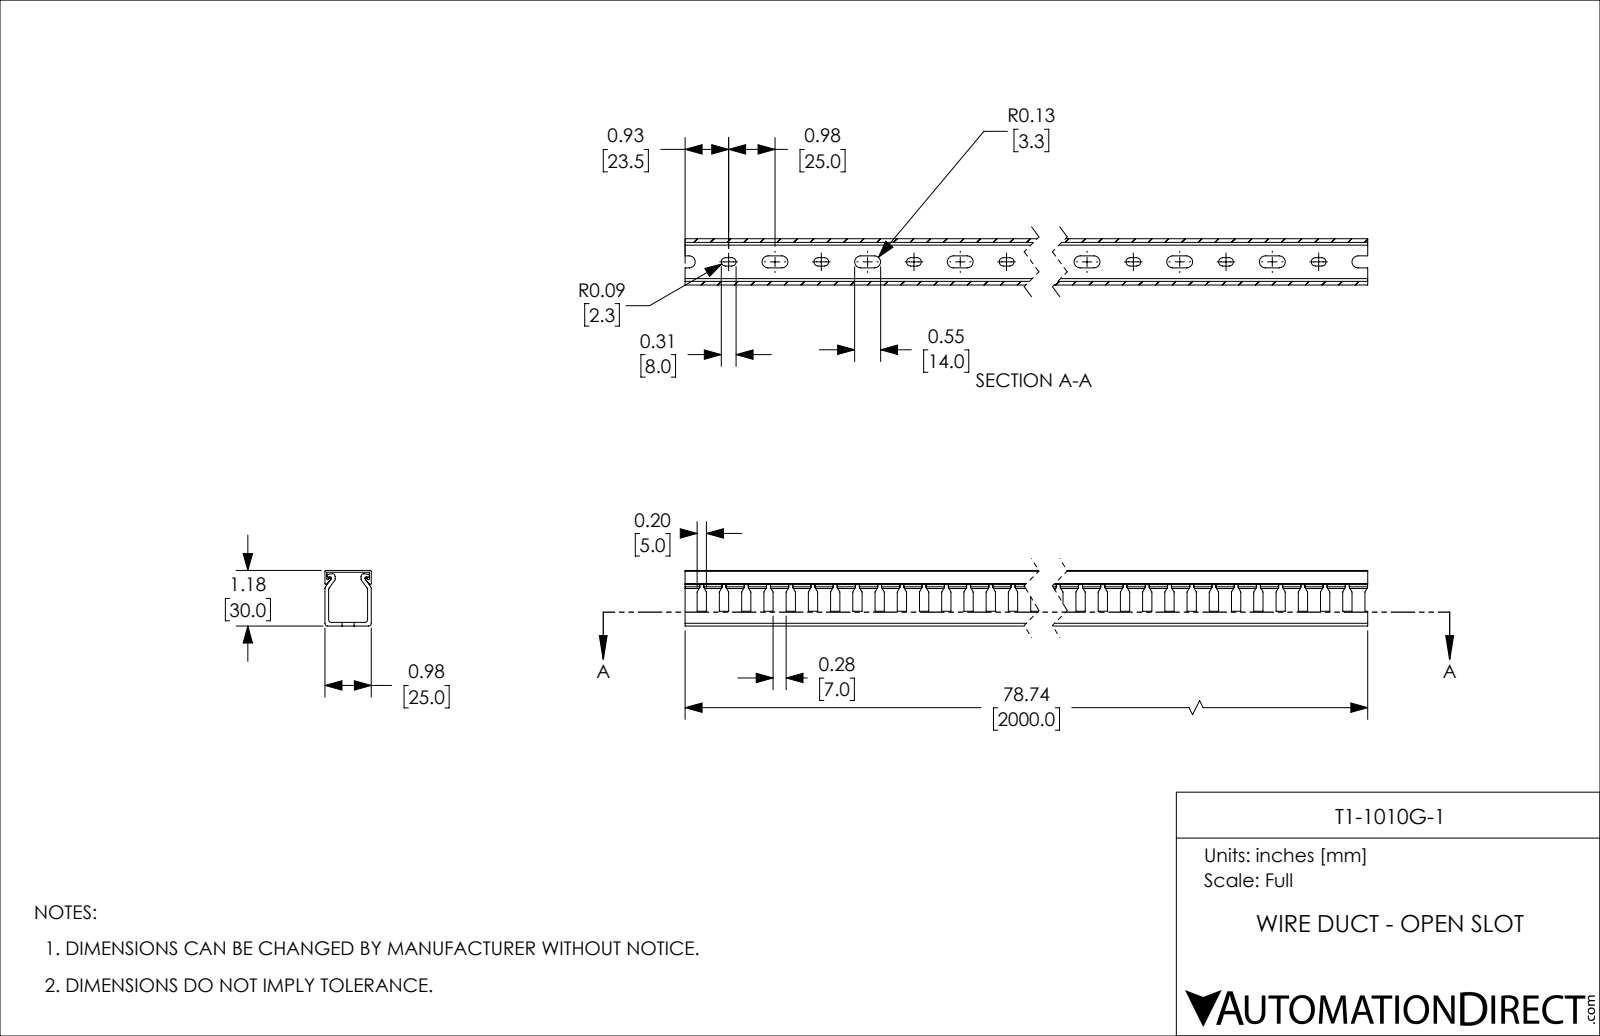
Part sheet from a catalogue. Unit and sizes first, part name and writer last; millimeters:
Units: millimetres
Overall size (bounding box): 2000 × 30 × 25
Partial cylindrical surfaces — rounded edges, fillets, slot ends (radius × count): R2.25 ×80, R3.25 ×80, R1.5 ×12, R0.5 ×8, R0.75 ×6
Main face-to-face distances: 2, 1, 23, 25, 29, 30, 21, 27, 28, 24
Volume: 407 568 mm³ · Surface area: 496 758 mm²
Bodies: 2 solids, 945 faces (514 planar, 431 cylindrical, 0 other)
Part name (STEP PRODUCT): T1-1010G-1
STEP written by: SolidWorks 2021 (CONFIG_CONTROL_DESIGN)
